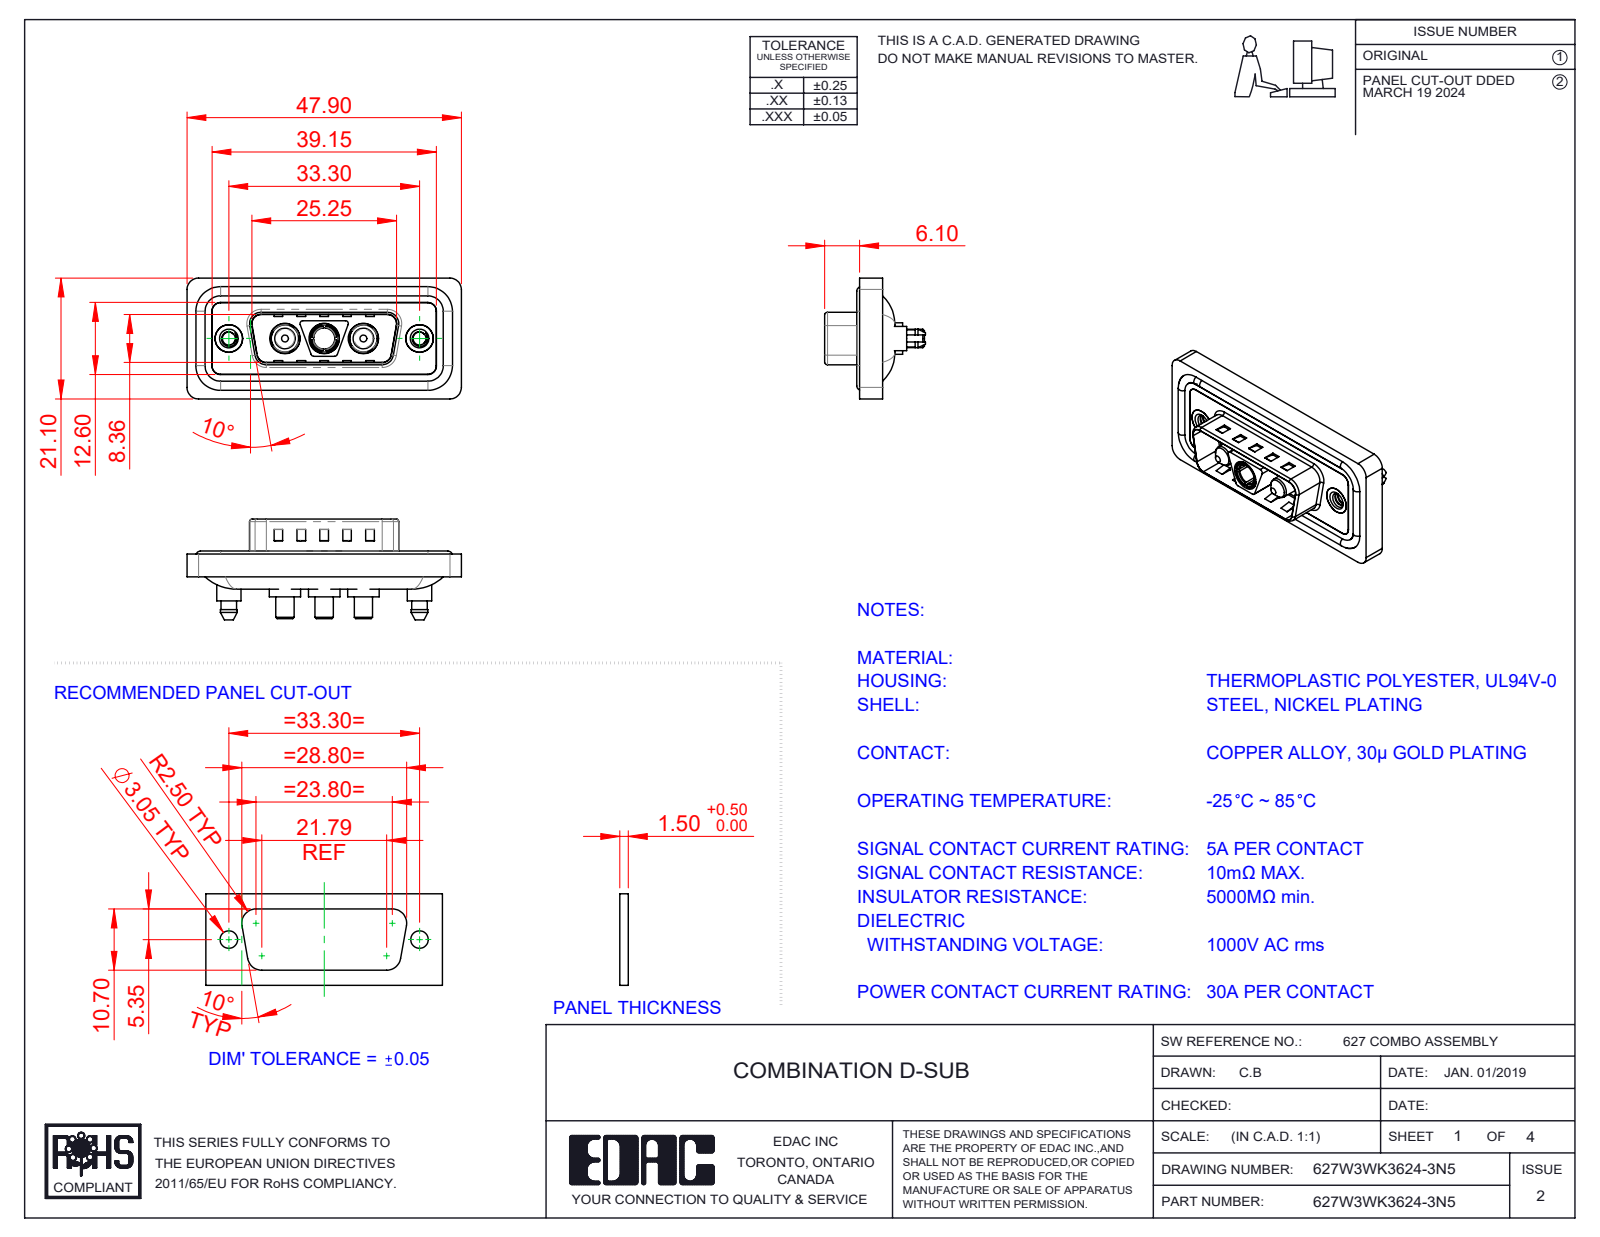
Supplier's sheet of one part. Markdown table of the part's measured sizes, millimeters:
| quantity | value |
| --- | --- |
| part name | 627Combo Shell Rear_15 Contacts; 627Combo Shell Front_15 Contacts; 627Combo Housing_3WK3; Power Pin_30A S (+4 more) |
| STEP written by | SolidWorks 2023 (CONFIG_CONTROL_DESIGN) |
| units | millimeters |
| bodies | 13 solids, 659 faces (247 planar, 282 cylindrical, 130 other) |
| overall size | 47.9 × 21.1 × 17.6 |
| volume | 5 843 mm³ |
| surface area | 9 474 mm² |
| round holes (diameter × count) | 4.85 × 3, 5.3 × 3, 2.26 × 2, 4 × 2, 4.8 × 2, 5 × 2, 3.7 × 1 |
| round bosses / shafts (diameter × count) | 1.6 × 4, 5.5 × 3, 5.2 × 3, 4.75 × 3, 3.75 × 3, 3.2 × 3, 5.4 × 2, 4.9 × 2 |
| partial cylindrical surfaces (radius × count) | 1.5 × 28, 2 × 20, 0.5 × 12, 1.6 × 10, 0.25 × 4, 0.6 × 4, 0.65 × 4, 0.9 × 4 |
| main face-to-face distances | 0.4, 1.1, 1.5, 0.5, 3.1, 1.6, 2.9, 4, 0.7, 0.82 |
| hole center spacings | 6.85, 9.8, 16.65, 23.5, 13.7, 33.3 |
